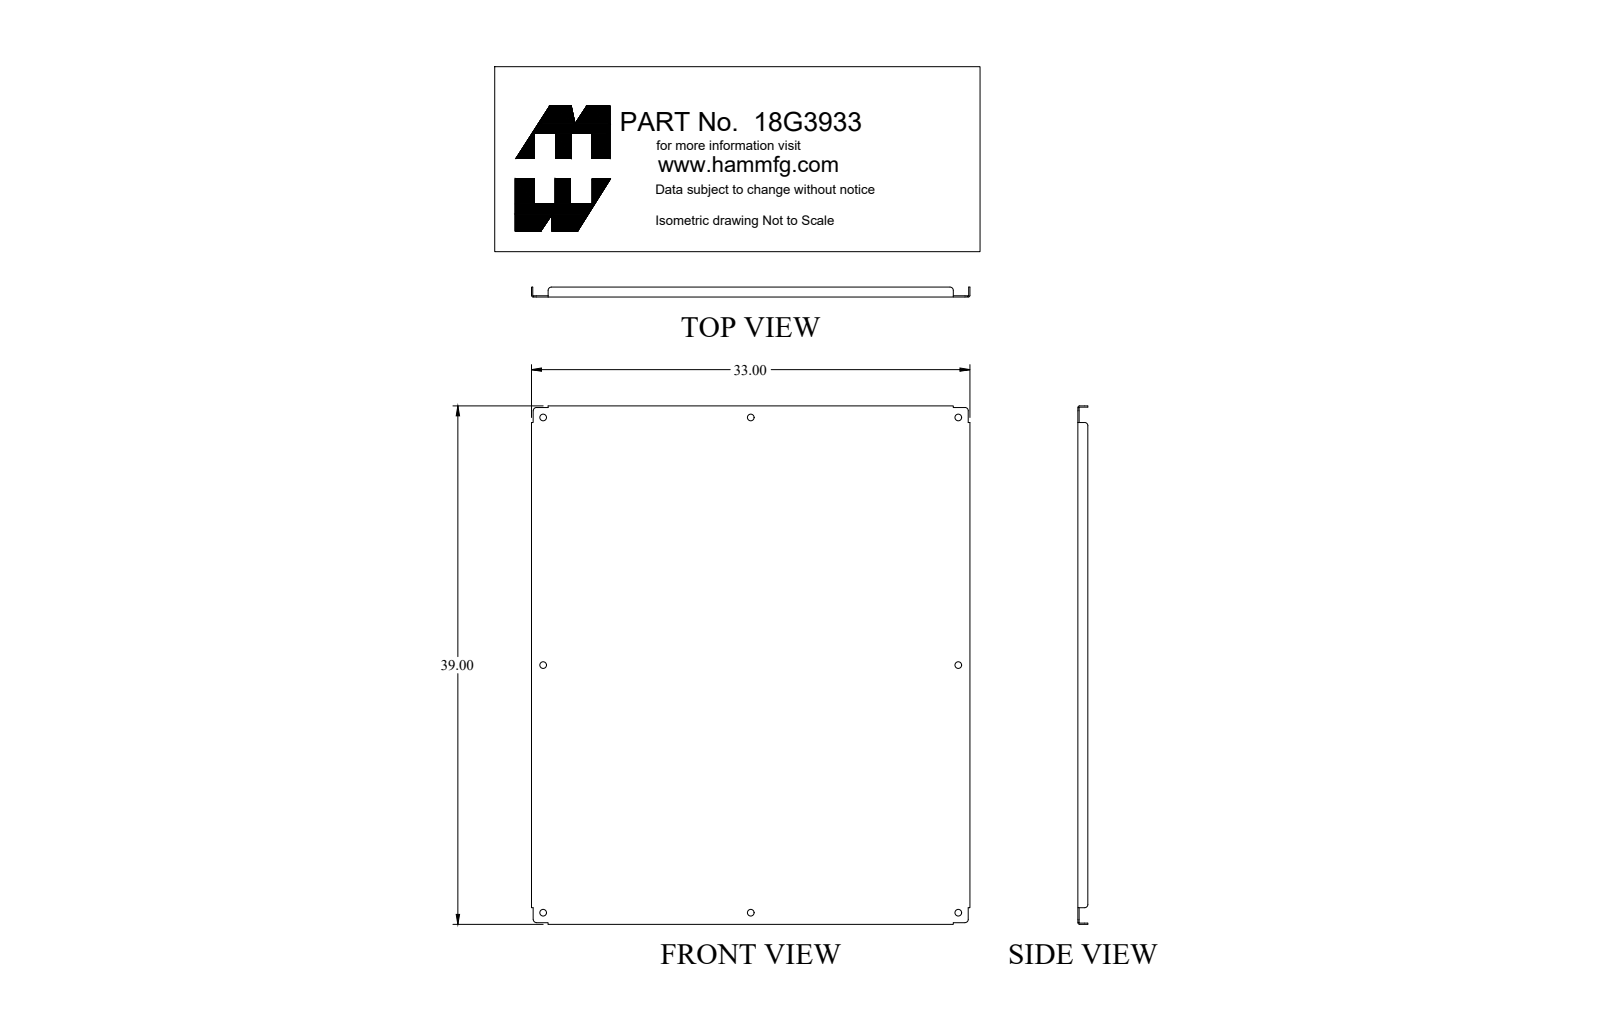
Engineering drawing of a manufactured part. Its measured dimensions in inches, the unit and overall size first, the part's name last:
Units: inches
Overall size (bounding box): 39 × 33 × 0.75
Round holes (diameter × count): ⌀0.5 ×8
Partial cylindrical surfaces — rounded edges, fillets, slot ends (radius × count): R0.25 ×8, R0.03 ×4, R0.125 ×4
Main face-to-face distances: 0.095, 32.905, 38.905, 33, 32.81, 39, 38.81, 0.75, 0.655, 0.125
Hole centre spacings: 15.625, 18.625, 24.311, 36.38, 40.394, 31.25, 37.25, 48.622
Volume: 129.9 in³ · Surface area: 2 750 in²
Bodies: 1 solid, 66 faces (30 planar, 36 cylindrical, 0 other)
Part name (STEP PRODUCT): 18G3933_Default
STEP written by: SolidWorks 2018 (CONFIG_CONTROL_DESIGN)
